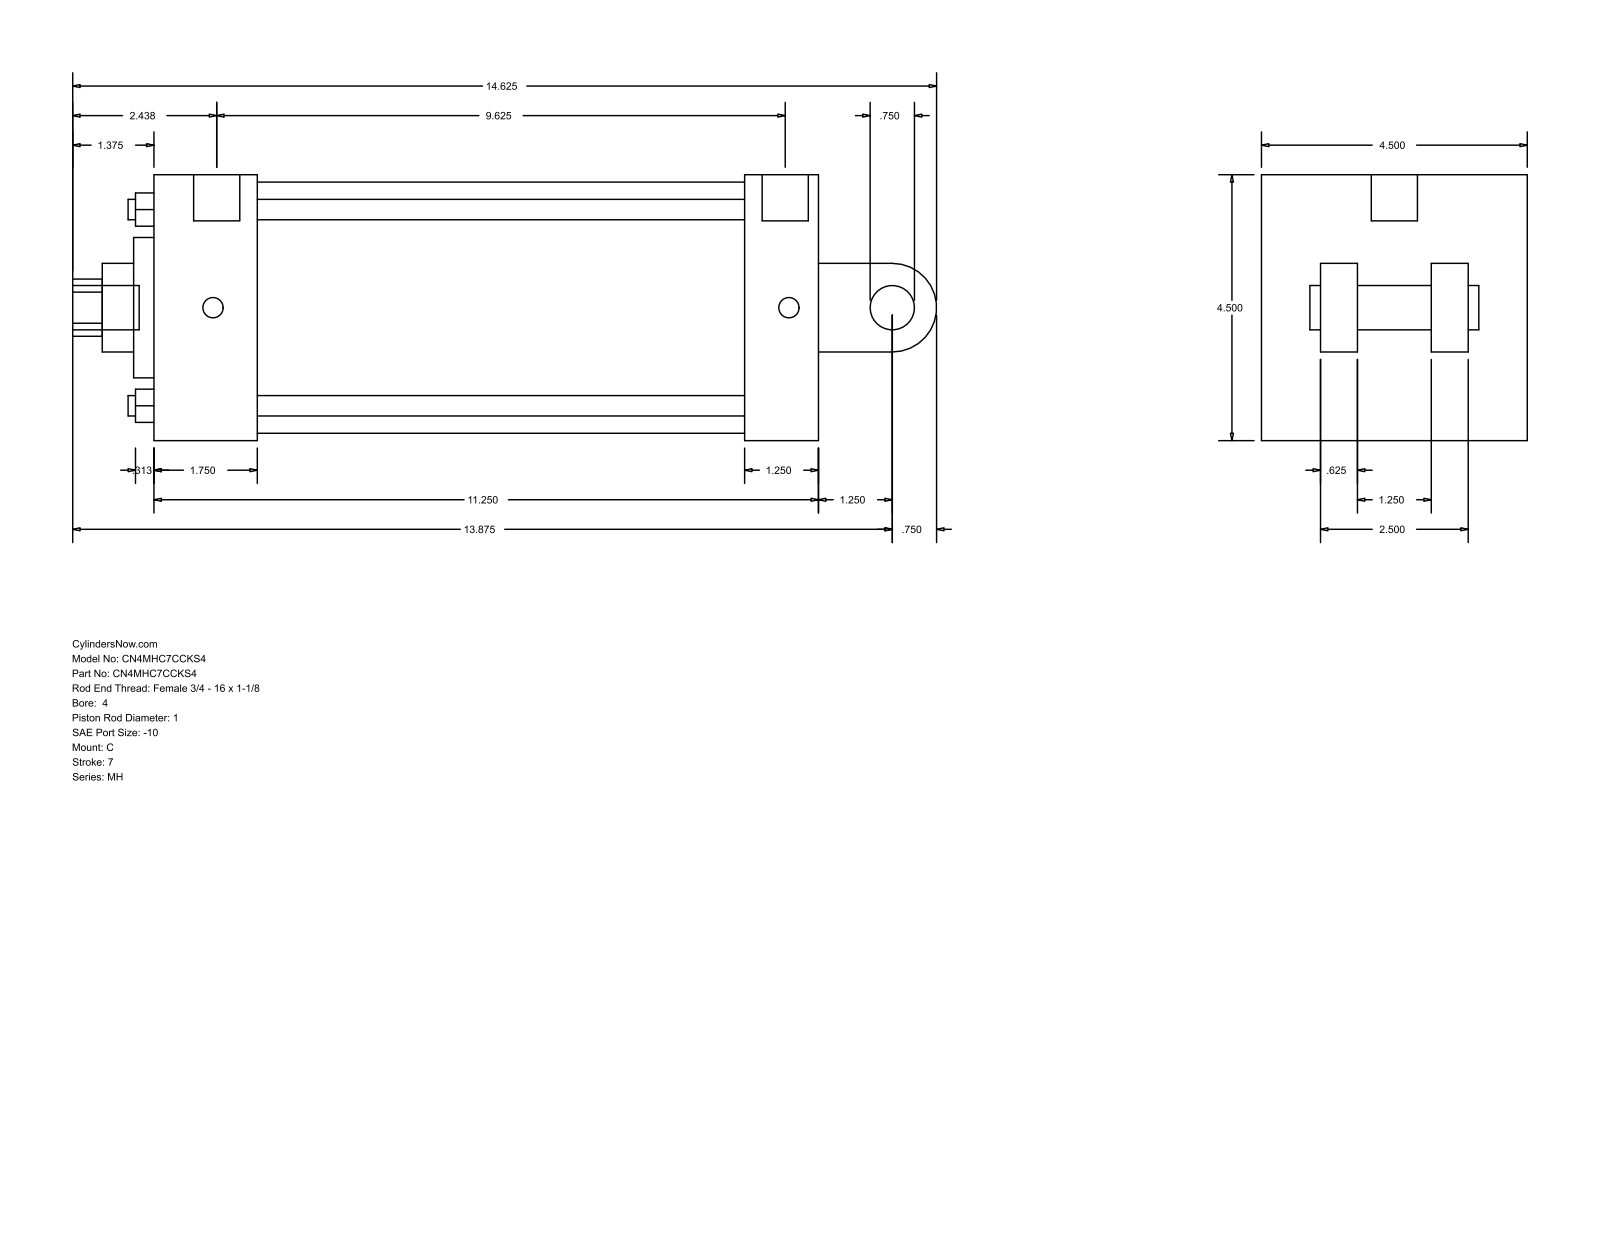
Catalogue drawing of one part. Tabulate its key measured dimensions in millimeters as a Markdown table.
| quantity | value |
| --- | --- |
| part name | MH_C__0400_1 |
| STEP written by | GSSL Pune (CONFIG_CONTROL_DESIGN) |
| units | millimeters |
| bodies | 0 solids, 101 faces (71 planar, 30 cylindrical, 0 other) |
| overall size | 371.48 × 114.3 × 114.3 |
| round holes (diameter × count) | 8.76 × 4, 8.73 × 2, 19.84 × 1, 25.4 × 1, 38.1 × 1, 60.33 × 1, 107.95 × 1 |
| round bosses / shafts (diameter × count) | 19.05 × 2, 8.73 × 2, 19.84 × 1 |
| partial cylindrical surfaces (radius × count) | 12.29 × 1, 19.05 × 1 |
| main face-to-face distances | 114.3, 285.76, 44.46, 254.01, 209.55, 241.3, 31.75, 73.03, 15.87, 47.63 |
| hole center spacings | 59.62, 84.32, 119.25, 1.59 |
